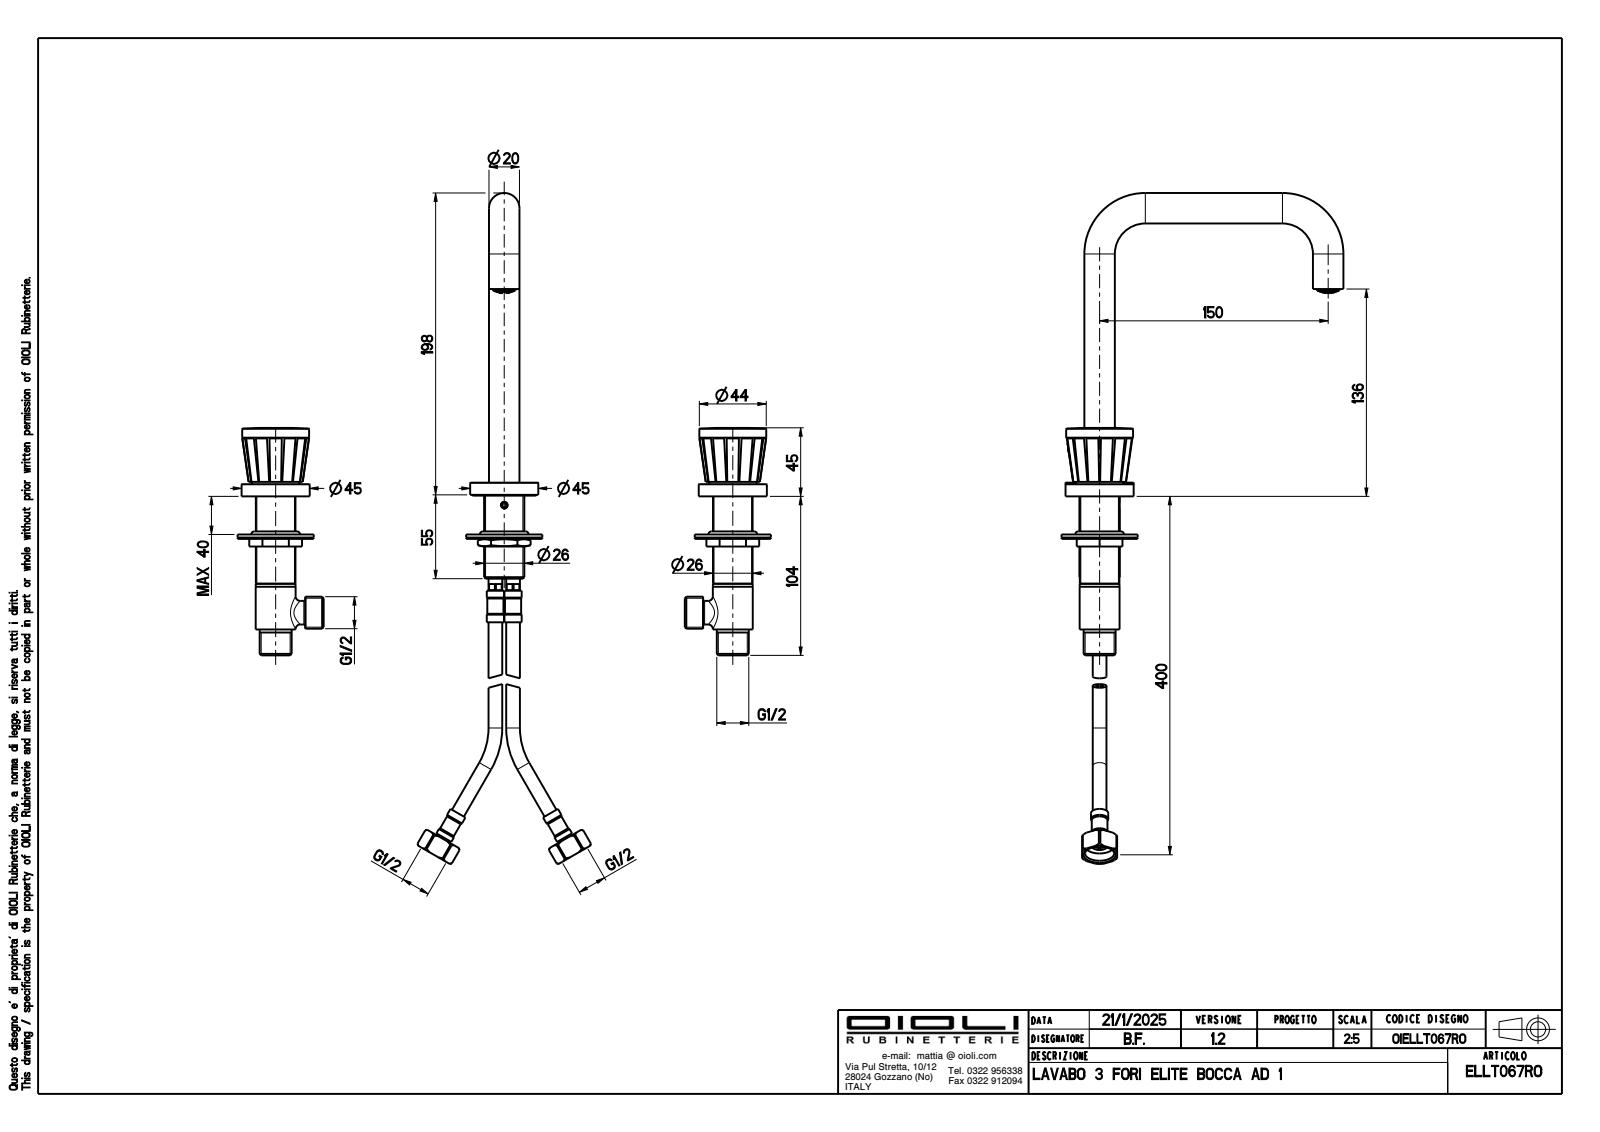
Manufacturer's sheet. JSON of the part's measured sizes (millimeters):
{"part_name": "OIBR00323; OICT00036; OIAR00087; OIVN00002 (+5 more)", "step_written_by": "CREO PARAMETRIC BY PTC INC, 2024493 (CONFIG_CONTROL_DESIGN)", "units": "millimeters", "bodies": {"solids": 15, "faces": 1221, "planar": 522, "cylindrical": 485, "other": 214}, "overall_size": [344.7, 213.5, 182.35], "volume_mm3": 119983, "surface_area_mm2": 99703, "round_holes": [[0.6, 81], [4.2, 4], [17, 3], [17.5, 3], [42, 3], [3, 2], [4, 2], [5.3, 2], [6.5, 2], [7, 2], [11, 2], [17.3, 2]], "round_bosses_or_shafts": [[44.7, 3], [36.5, 3], [20, 3], [18.5, 3], [43.9, 2], [31, 2], [26, 2], [24, 2]], "partial_cylinders_radius": [[0.1, 18], [1, 8], [0.2, 4], [0.5, 4], [1.2, 4], [2, 4], [3, 4], [3.85, 2]], "face_to_face_distances": [8, 1, 9, 42, 34, 33, 2.1, 5.9, 7, 3.7], "hole_center_spacings": [4.97, 3.31, 5.97, 1.29, 1.65, 4.38, 4.96, 1.3]}
